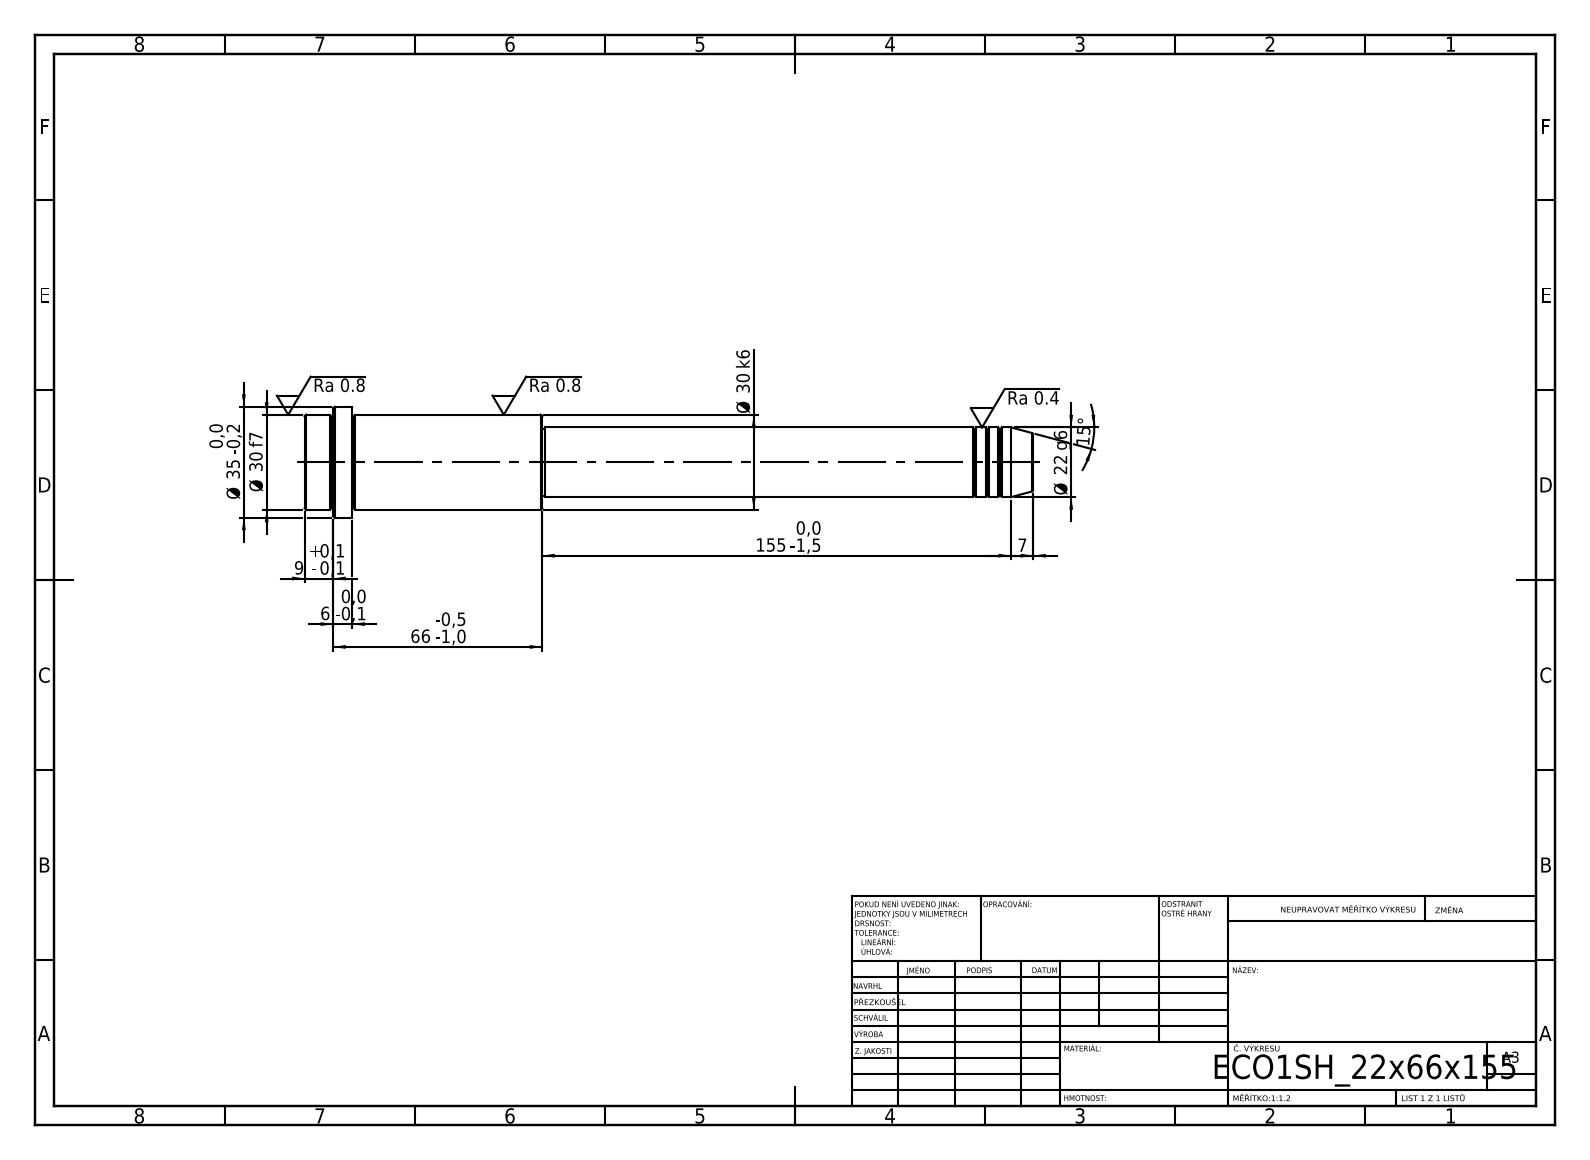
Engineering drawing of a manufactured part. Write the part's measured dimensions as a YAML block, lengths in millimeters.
step_written_by: "SolidWorks 2019 (CONFIG_CONTROL_DESIGN)"
units: millimeters
bodies: {solids: 1, faces: 52, planar: 6, cylindrical: 16, other: 30}
overall_size: [230, 35, 35]
volume: 112813
surface_area: 19835
round_bosses_or_shafts:
  - {diameter: 35, count: 1}
  - {diameter: 30, count: 1}
  - {diameter: 22, count: 1}
  - {diameter: 21, count: 1}
face_to_face_distances: [75, 60, 15, 155, 215, 230, 221, 66, 6, 9]
